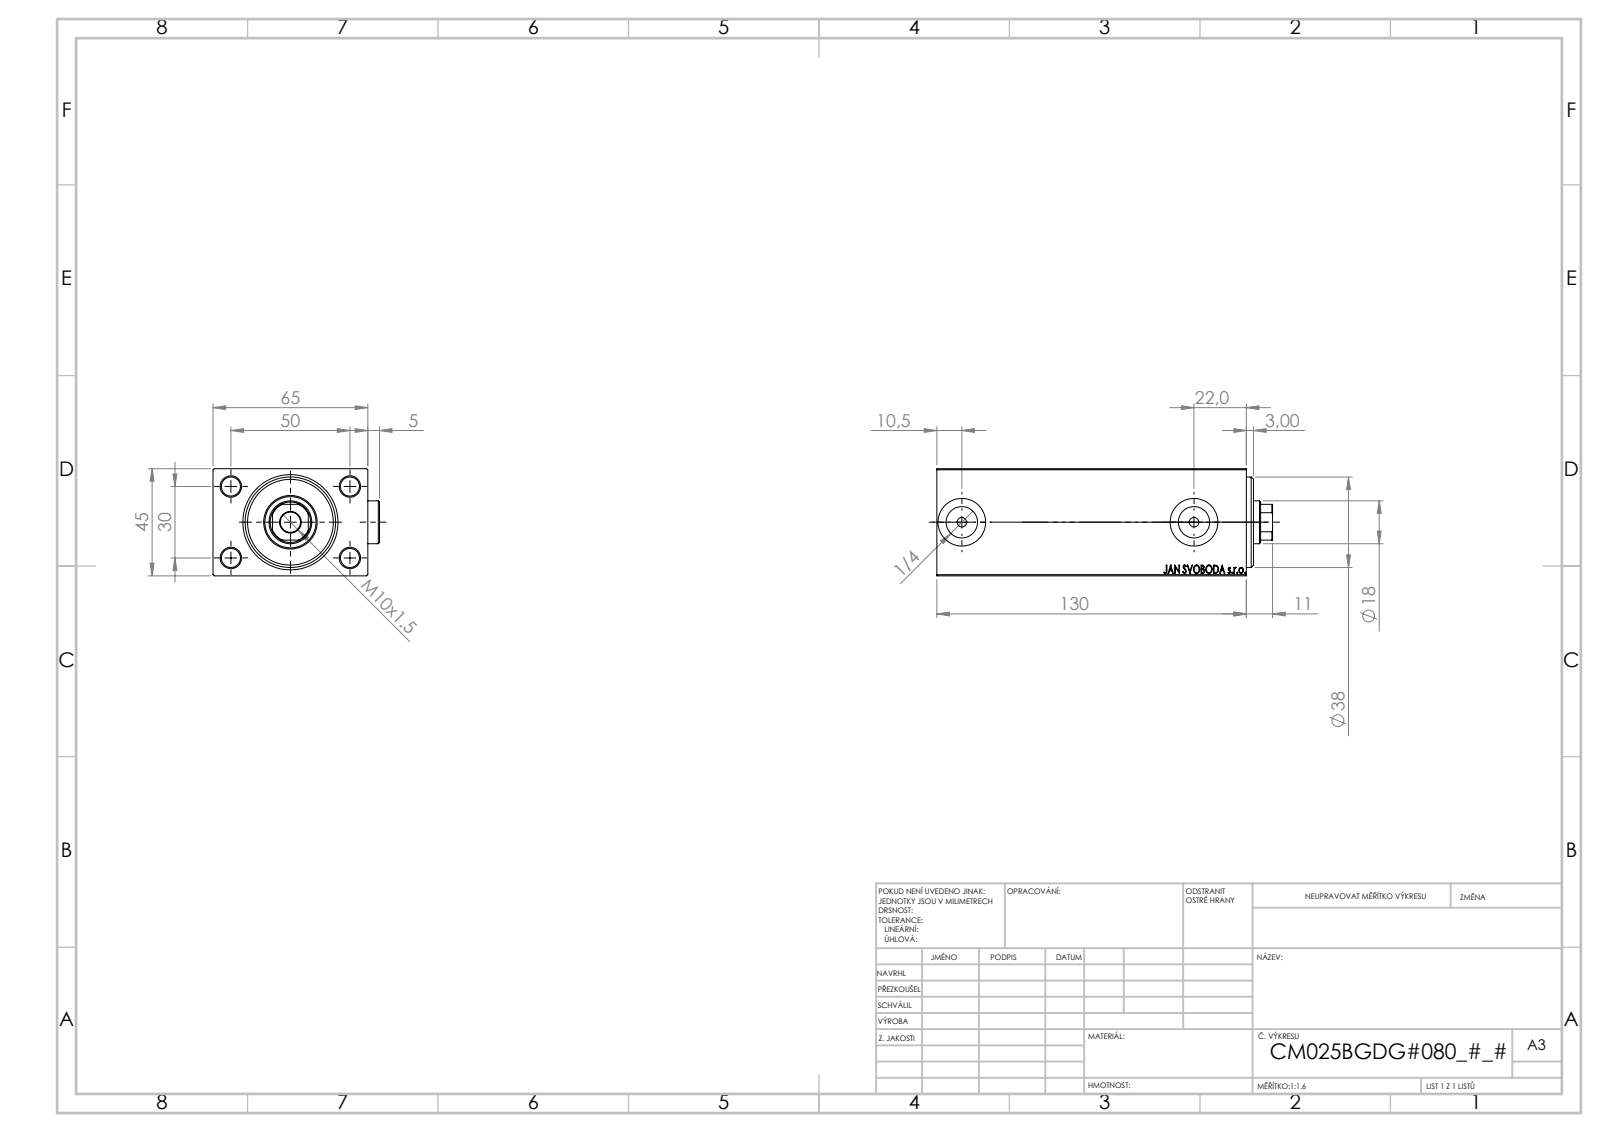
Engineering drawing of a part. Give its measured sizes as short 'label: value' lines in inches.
name: V450CM_VC_B; V450CM_B_Body; Zatka_OIL_PORT; V450CM_B_VCP
written by: SolidWorks 2019 (CONFIG_CONTROL_DESIGN)
unit: in
bodies: 4 solids, 935 faces (435 planar, 70 cylindrical, 430 other)
size: 5.551 × 2.752 × 1.772
volume: 3.176 in³; area: 85.71 in²
holes: 4× ⌀0.315, 2× ⌀0.157, 2× ⌀0.518, 2× ⌀0.787, 1× ⌀0.335, 1× ⌀0.709, 1× ⌀0.846, 1× ⌀0.886, 1× ⌀0.984, 1× ⌀1.063, 1× ⌀1.496
bosses: 2× ⌀0.709
rounds: 1× R0.335
face distances: 1.772, 4.685, 0.315, 5, 2.555, 0.236, 0.551, 2.551, 4.449, 0.197
hole spacings: 1.148, 1.181, 1.969, 2.296, 3.839
